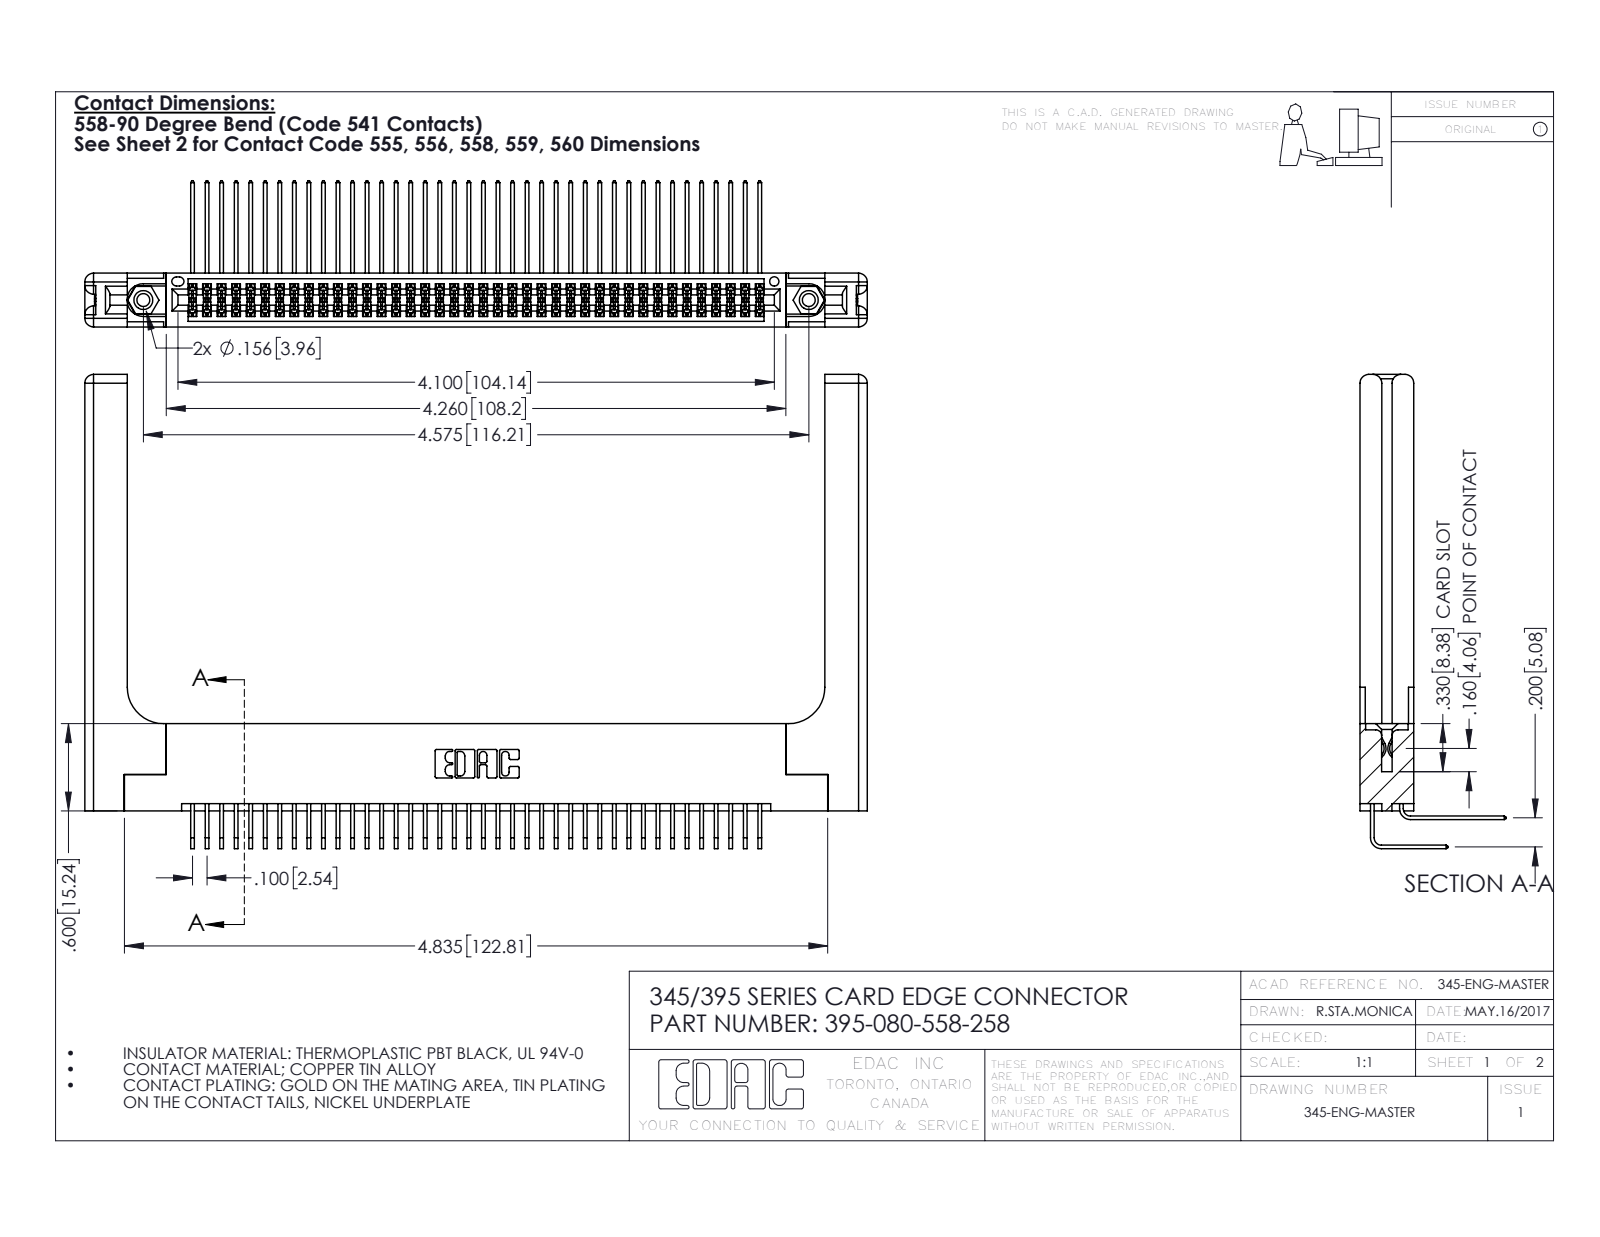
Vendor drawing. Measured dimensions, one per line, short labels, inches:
name: 345-250-001_345-250-001-102; 345-292-001_558 559 Tail - 1; 345-292-001_558 Tail - 2; 345 Part_Flush Mounting Lugs - 0.156 Dia-TH (+2 more)
written by: SolidWorks 2016 (CONFIG_CONTROL_DESIGN)
unit: in
bodies: 85 solids, 4542 faces (3028 planar, 1454 cylindrical, 60 other)
size: 5.379 × 3.259 × 1.005
volume: 1.354 in³; area: 42.57 in²
holes: 2× ⌀0.089, 2× ⌀0.125, 2× ⌀0.156, 1× ⌀0.064
bosses: 2× ⌀0.155
rounds: 121× R0.006, 22× R0.01, 16× R0.06, 6× R0.007, 6× R0.031, 3× R0.026, 2× R0.014, 2× R0.019
face distances: 0.072, 0.37, 0.298, 0.2, 0.098, 0.272, 0.025, 0.225, 0.148, 0.15
hole spacings: 0.27, 4.339, 4.575
